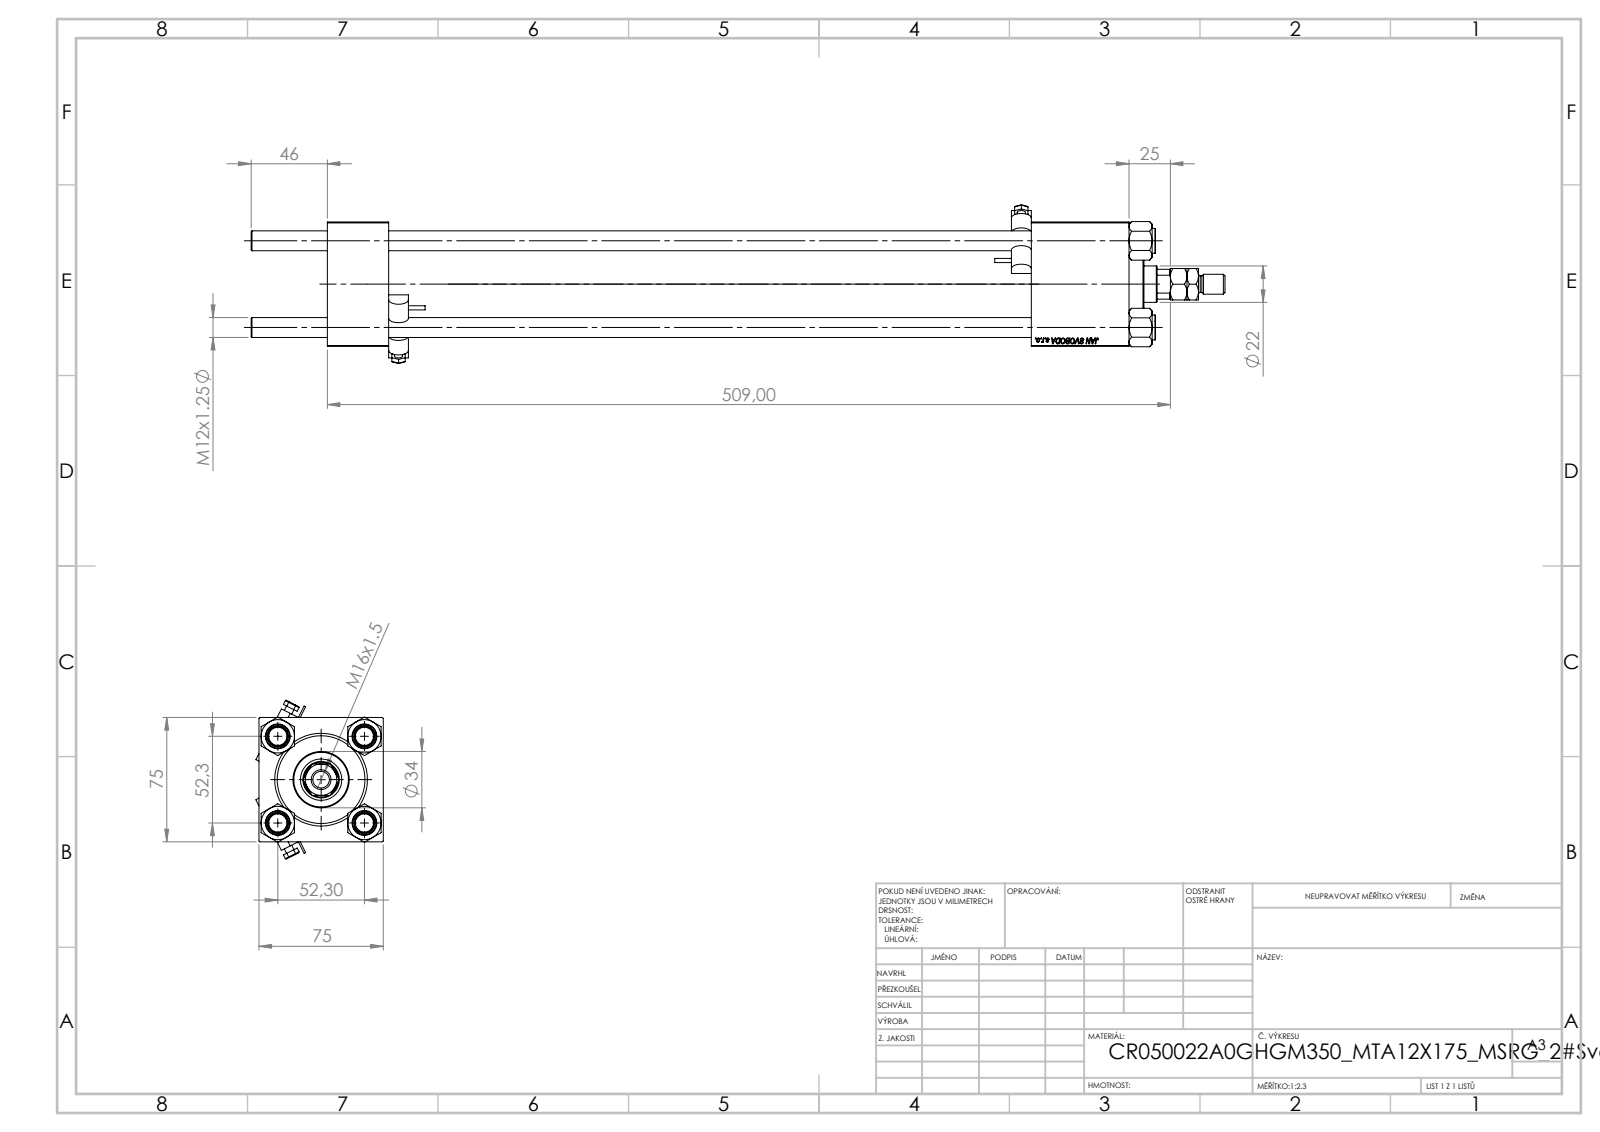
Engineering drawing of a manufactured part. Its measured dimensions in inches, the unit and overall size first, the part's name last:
Units: inches
Overall size (bounding box): 23.15 × 3.772 × 3.027
Round holes (diameter × count): ⌀0.472 ×4, ⌀0.276 ×2, ⌀0.825 ×2, ⌀1.181 ×2, ⌀0.413 ×1, ⌀0.866 ×1, ⌀0.984 ×1, ⌀1.614 ×1, ⌀1.969 ×1, ⌀2.087 ×1
Round bosses / shafts (diameter × count): ⌀0.591 ×4, ⌀0.197 ×2, ⌀0.098 ×2, ⌀2.205 ×1, ⌀1.339 ×1, ⌀0.472 ×1, ⌀0.394 ×1
Partial cylindrical surfaces — rounded edges, fillets, slot ends (radius × count): R0.02 ×12, R0.236 ×4, R0.413 ×1
Main face-to-face distances: 2.953, 1.457, 19.055, 17.598, 16.732, 15.276, 2.323, 17.925, 16.469, 1.193
Hole centre spacings: 1.456, 2.059, 2.912, 16.673
Volume: 69.81 in³ · Surface area: 547.2 in²
Bodies: 14 solids, 1247 faces (571 planar, 110 cylindrical, 566 other)
Part name (STEP PRODUCT): MTA; MSRF_MSRG1; NUT_M5; CR025_012_A_0_G_A_G_M_020_+#_##_TYCINKA (+3 more)
STEP written by: SolidWorks 2019 (CONFIG_CONTROL_DESIGN)
